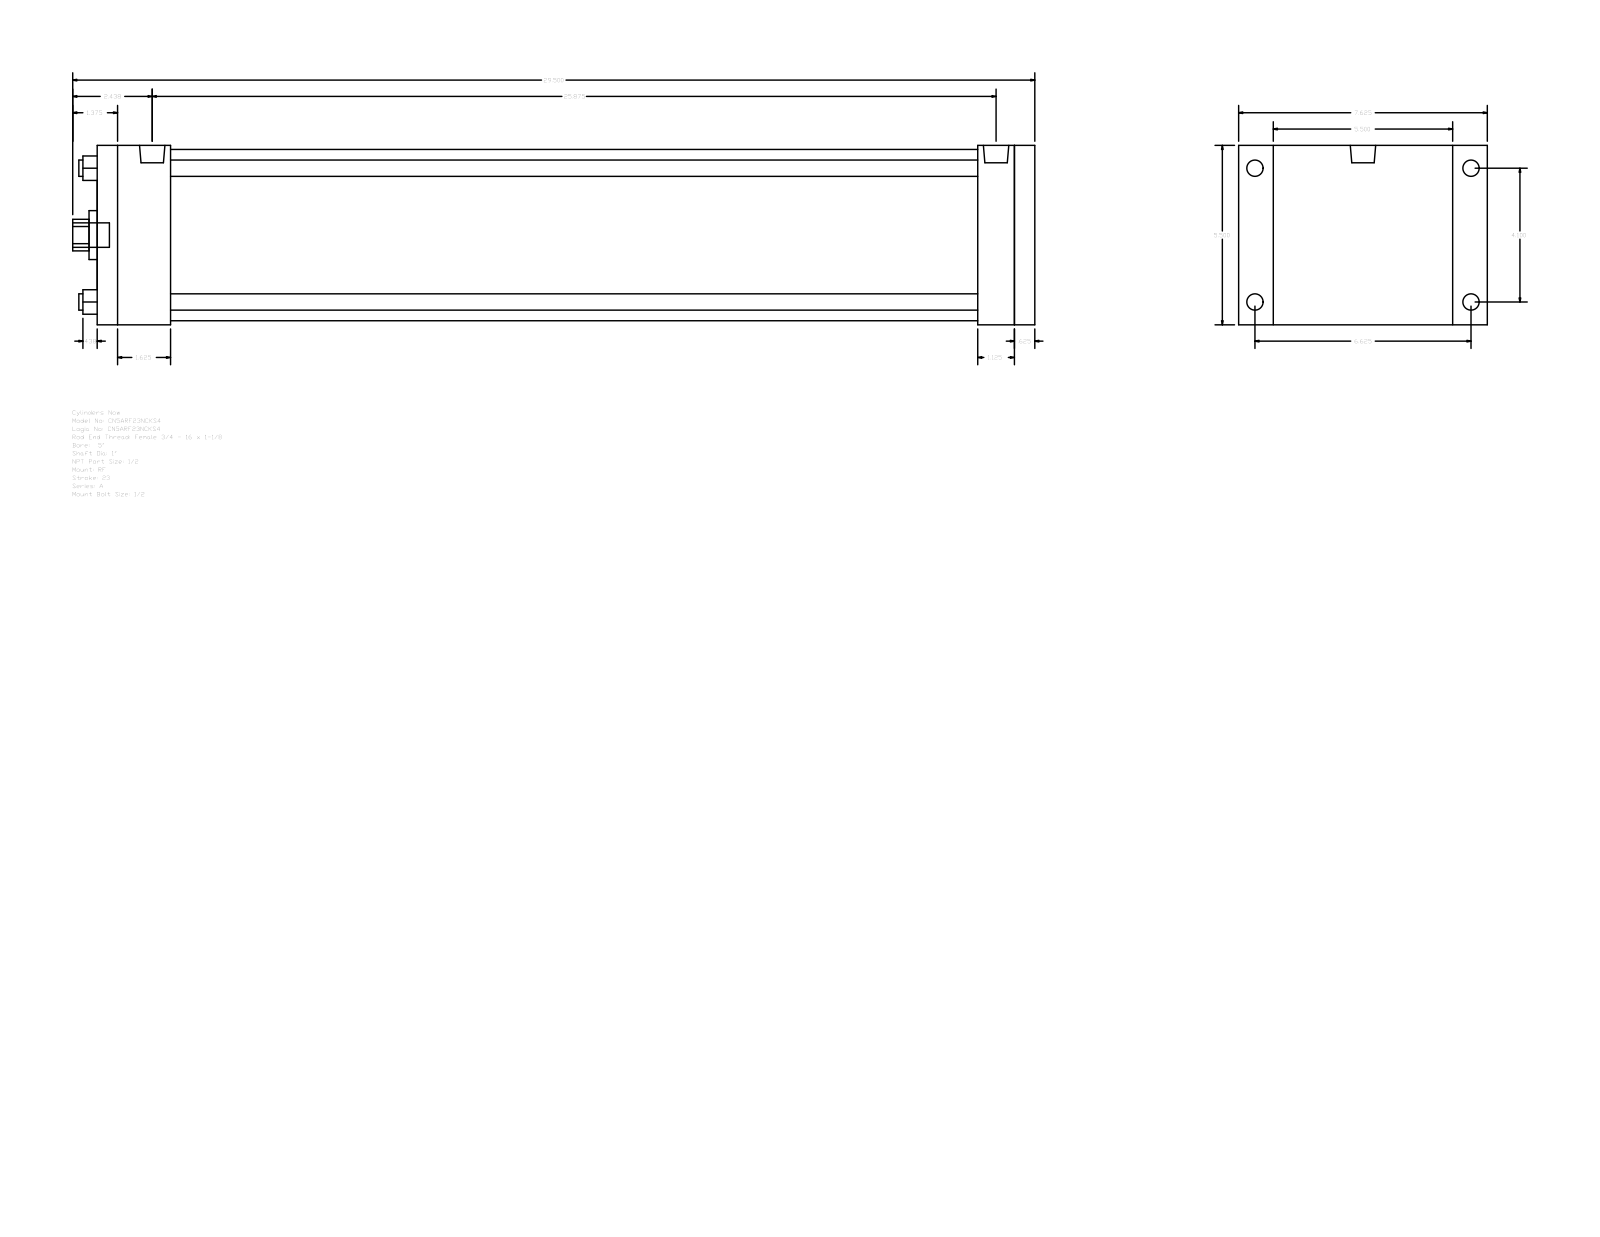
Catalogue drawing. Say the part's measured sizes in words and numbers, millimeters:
The part is named "A_RF__0500_1". Its 3-D file was written by "GSSL Pune (CONFIG_CONTROL_DESIGN)". It is 0 solids with 92 faces: 64 planar, 28 cylindrical and 0 other. Overall it measures 749.3 by 193.68 by 139.7 millimeters. Round holes: 4 of diameter 12.7, 1 of diameter 25.4, 1 of diameter 38.1, 1 of diameter 133.35. Round bosses or shafts: 4 of diameter 12.7, 4 of diameter 8.73, 2 of diameter 19.77, 1 of diameter 19.05. Partial cylindrical surfaces (rounded edges, fillets, slot ends): 1 of radius 12.29. The main face-to-face distances are 139.7, 730.25, 714.37, 15.88, 28.57, 57.15, 657.22, 673.1, 685.8, 628.65. The hole center spacings are 73.64, 104.14, 147.28.
